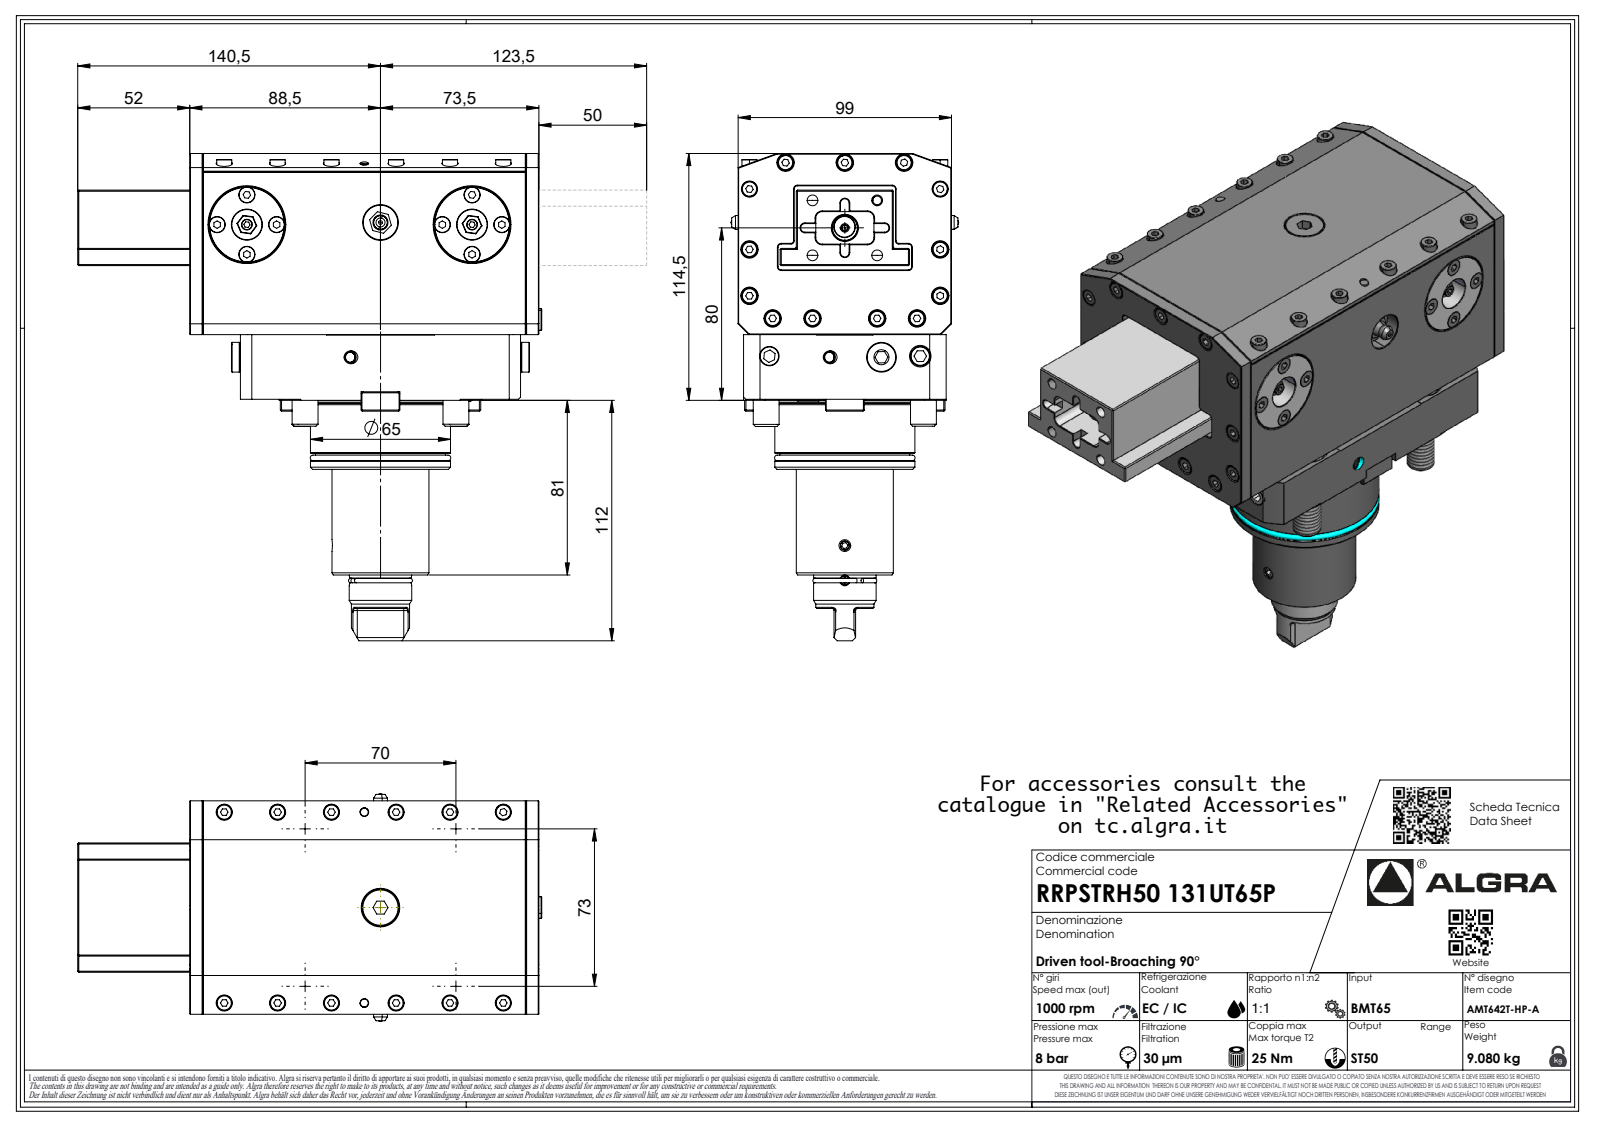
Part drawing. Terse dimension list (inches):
name: RRPSTRH50131UT65P
written by: SolidWorks 2023 (AUTOMOTIVE_DESIGN)
unit: in
bodies: 1 solid, 773 faces (466 planar, 112 cylindrical, 195 other)
size: 8.898 × 8.478 × 4.157
volume: 121.2 in³; area: 218.2 in²
holes: 1× ⌀0.083, 1× ⌀0.394
bosses: 12× ⌀0.276, 1× ⌀2.559, 1× ⌀2.543, 1× ⌀2.374, 1× ⌀1.772, 1× ⌀1.142, 1× ⌀1.063, 1× ⌀0.512
rounds: 12× R0.098, 7× R0.013, 7× R0.02, 7× R0.146, 6× R0.039, 4× R0.394, 2× R0.079, 1× R0.008
face distances: 3.898, 0.021, 0.285, 0.264, 3.799, 0.098, 6.378, 2.047, 1.201, 3.022
